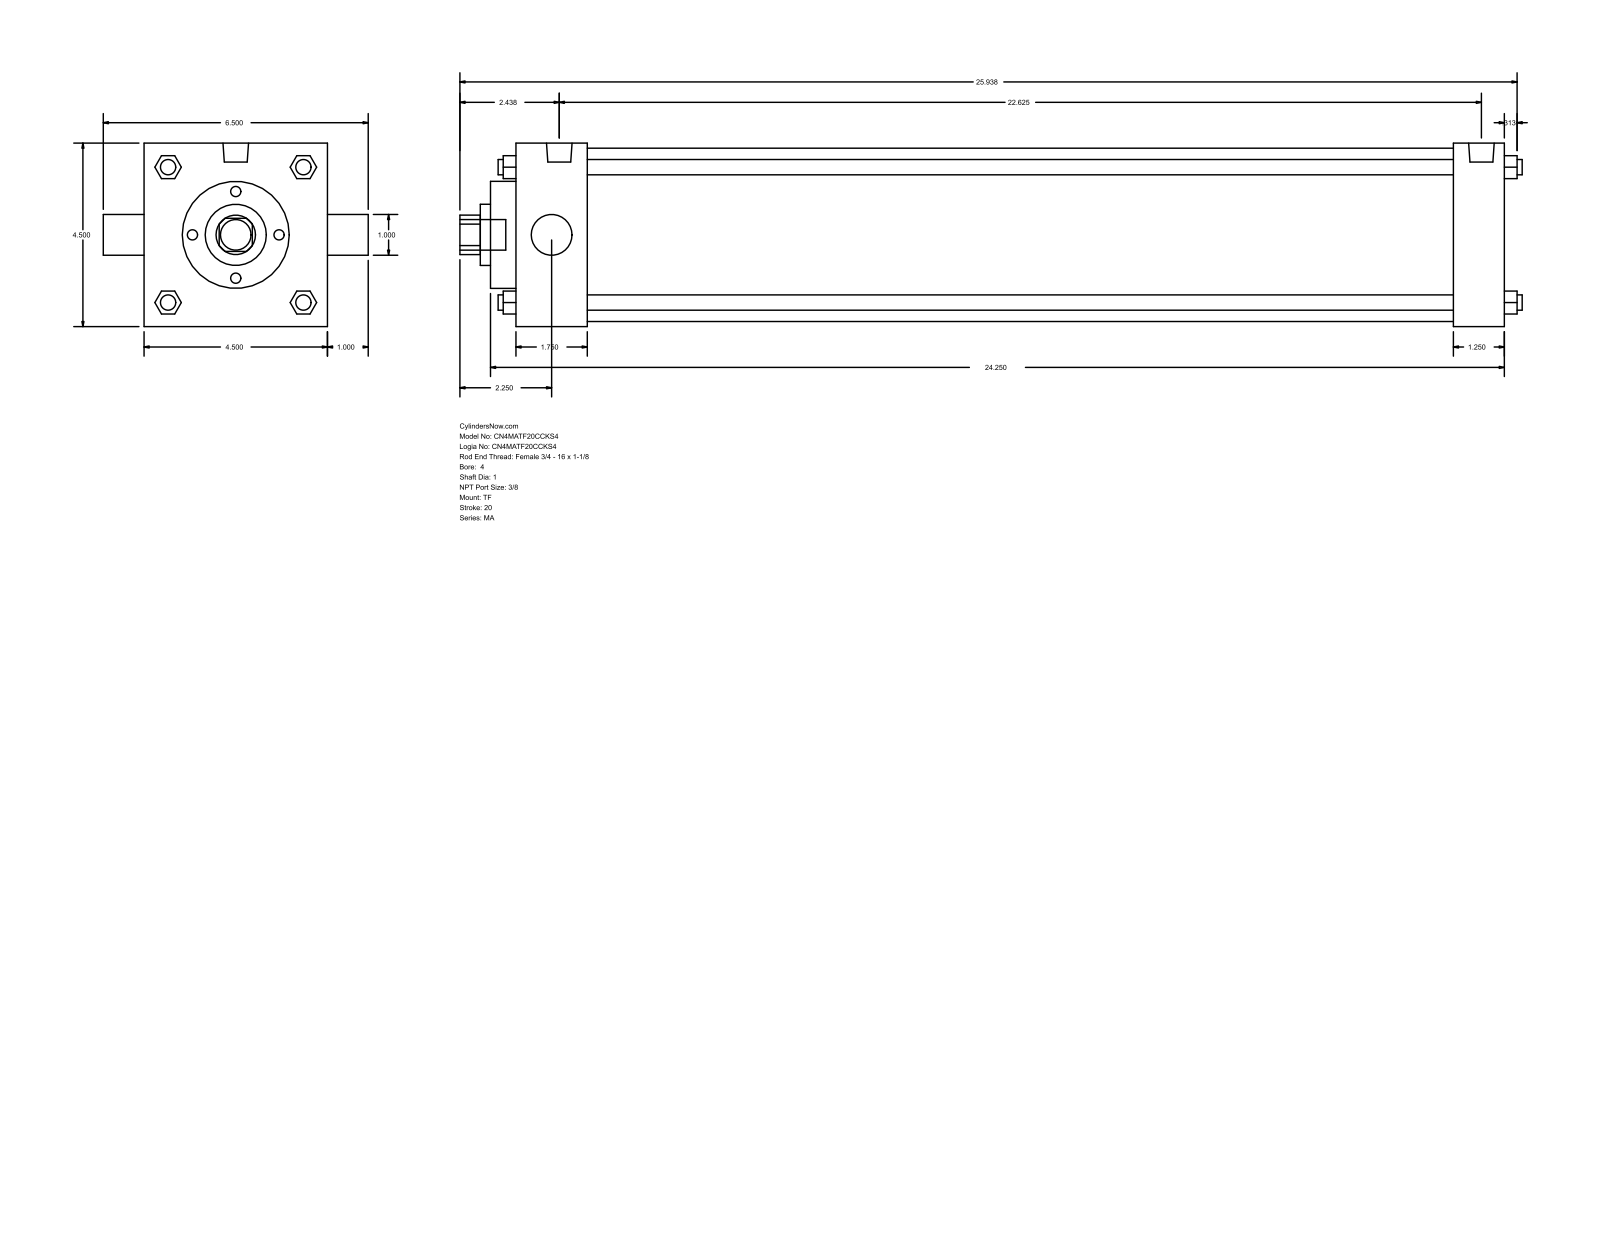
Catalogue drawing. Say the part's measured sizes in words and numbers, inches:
The part is named "MA_TF__0400_1". Its 3-D file was written by "GSSL Pune (CONFIG_CONTROL_DESIGN)". It is 0 solids with 122 faces: 93 planar, 29 cylindrical and 0 other. Overall it measures 26.063 by 6.5 by 4.5 inches. Round holes: 2 of diameter 1, 1 of diameter 1.5, 1 of diameter 2.625, 1 of diameter 4.25. Round bosses or shafts: 4 of diameter 0.375, 3 of diameter 0.437, 2 of diameter 0.627, 1 of diameter 0.75. Partial cylindrical surfaces (rounded edges, fillets, slot ends): 1 of radius 0.484. The main face-to-face distances are 4.5, 24.25, 23, 1.25, 1.75, 21.25, 22.5, 0.625, 2.375, 23.625.
